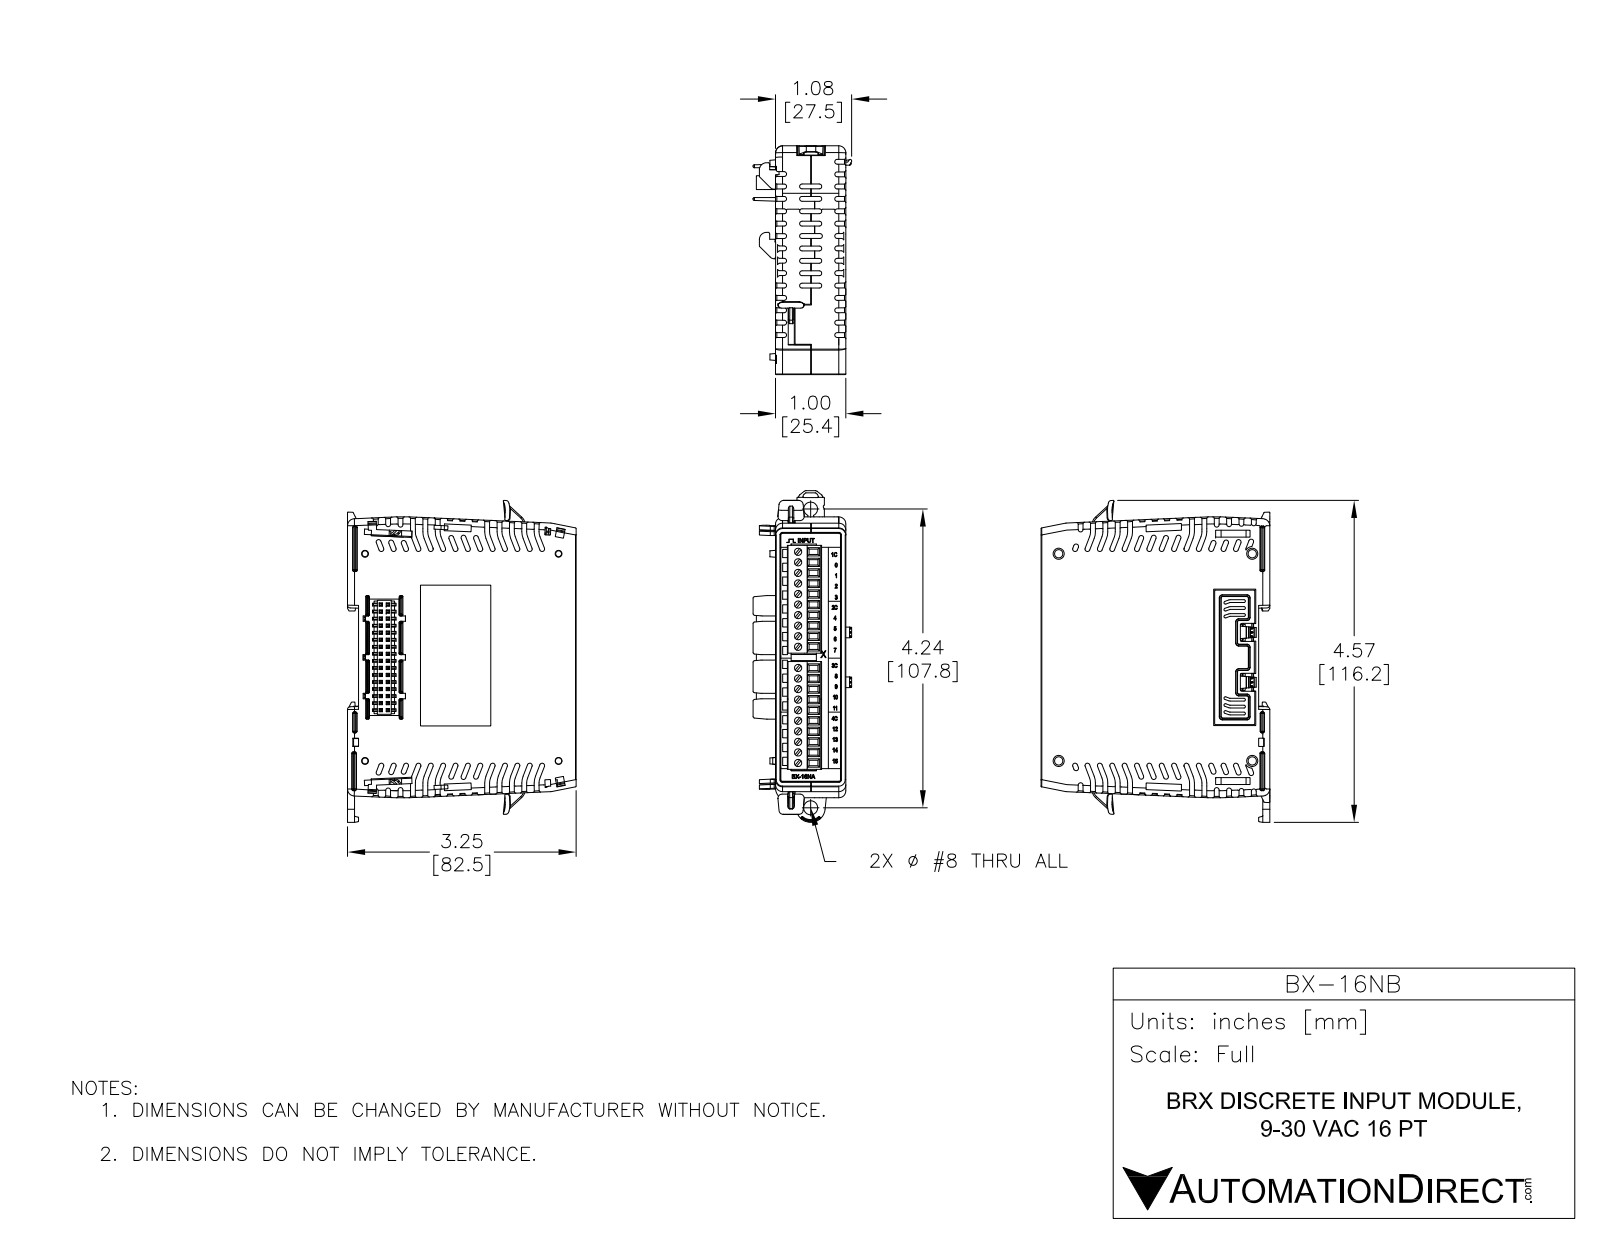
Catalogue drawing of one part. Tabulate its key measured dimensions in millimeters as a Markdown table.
| quantity | value |
| --- | --- |
| part name | BX-16NB |
| STEP written by | SolidWorks 2017 (AUTOMOTIVE_DESIGN) |
| units | millimeters |
| bodies | 12 solids, 4157 faces (2930 planar, 663 cylindrical, 564 other) |
| overall size | 116.5 × 82.6 × 35.6 |
| volume | 189 800 mm³ |
| surface area | 46 780 mm² |
| round holes (diameter × count) | 1.2 × 2, 1.7 × 2, 3 × 2, 3 × 2, 5.1 × 1 |
| round bosses / shafts (diameter × count) | 1.6 × 2, 1.5 × 2 |
| partial cylindrical surfaces (radius × count) | 0.1 × 102, 0.2 × 101, 0.3 × 47, 0.5 × 34, 0.1 × 24, 1.6 × 20, 3 × 14, 1 × 13 |
| main face-to-face distances | 25.4, 81.6, 81.8, 12.1, 1, 4, 77.5, 77.8, 2.5, 20 |
| hole center spacings | 2.5, 20.9, 23.3, 33, 53.2, 55.7, 65.7, 66.5 |
